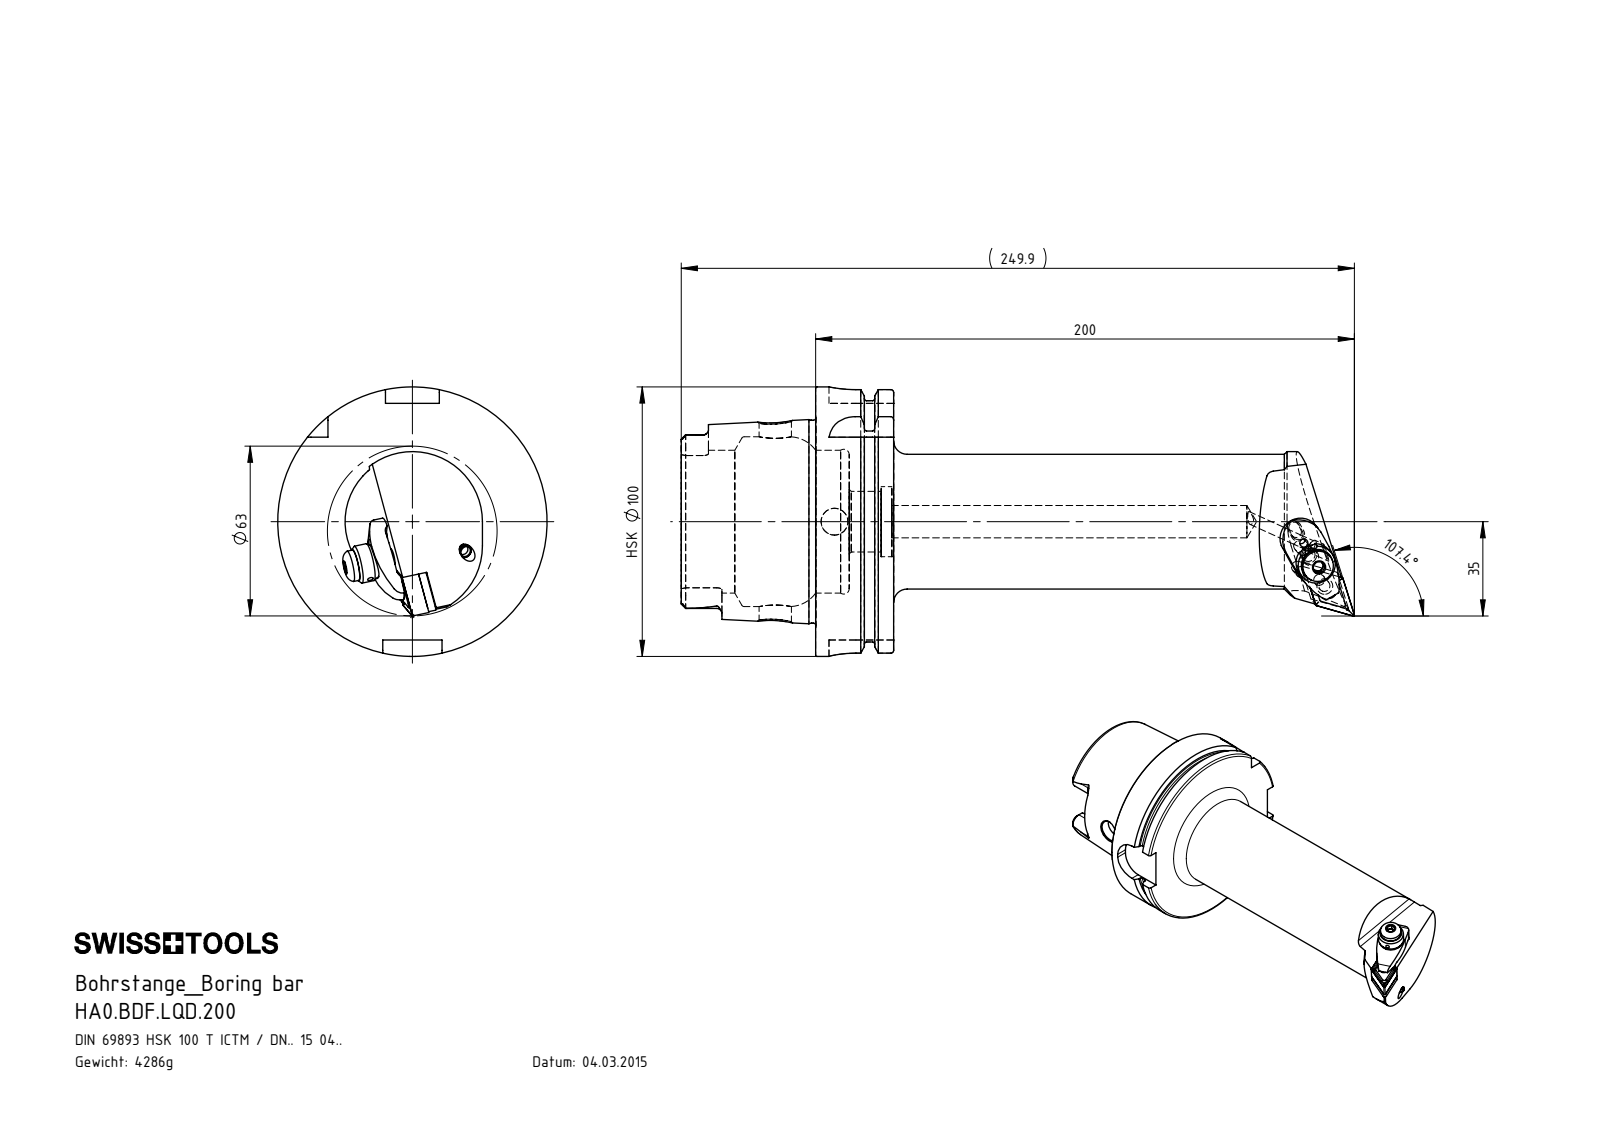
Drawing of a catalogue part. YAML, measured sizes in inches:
part_name: "WCC-ER5.102.005_A; WCC-ER4.103.032_A; WCC-ER3.102.024_C; DNMG150604 (+6 more)"
step_written_by: "SolidWorks 2017 (AUTOMOTIVE_DESIGN)"
units: inches
bodies: {solids: 10, faces: 329, planar: 114, cylindrical: 100, other: 115}
overall_size: [9.839, 3.937, 3.937]
volume: 33.66
surface_area: 132.8
round_holes:
  - {diameter: 0.079, count: 3}
  - {diameter: 0.165, count: 2}
  - {diameter: 0.197, count: 2}
  - {diameter: 0.276, count: 2}
  - {diameter: 0.472, count: 2}
  - {diameter: 0.118, count: 1}
  - {diameter: 0.157, count: 1}
  - {diameter: 0.203, count: 1}
  - {diameter: 0.244, count: 1}
  - {diameter: 0.252, count: 1}
  - {diameter: 0.335, count: 1}
  - {diameter: 0.394, count: 1}
round_bosses_or_shafts:
  - {diameter: 0.197, count: 2}
  - {diameter: 3.937, count: 1}
  - {diameter: 3.62, count: 1}
  - {diameter: 2.963, count: 1}
  - {diameter: 1.969, count: 1}
  - {diameter: 0.551, count: 1}
  - {diameter: 0.453, count: 1}
  - {diameter: 0.276, count: 1}
partial_cylinders:
  - {radius: 0.015, count: 6}
  - {radius: 0.075, count: 6}
  - {radius: 0.016, count: 4}
  - {radius: 0.039, count: 4}
  - {radius: 0.394, count: 4}
  - {radius: 0.027, count: 3}
  - {radius: 0.027, count: 3}
  - {radius: 0.059, count: 3}
face_to_face_distances: [1.14, 0.49, 0.65, 1.965, 2.455, 3.104, 3.457, 0.624, 3.079, 1.114]
hole_center_spacings: [0.589, 0.315, 0.316, 0.323, 0.583, 0.583, 0.591, 0.591]
